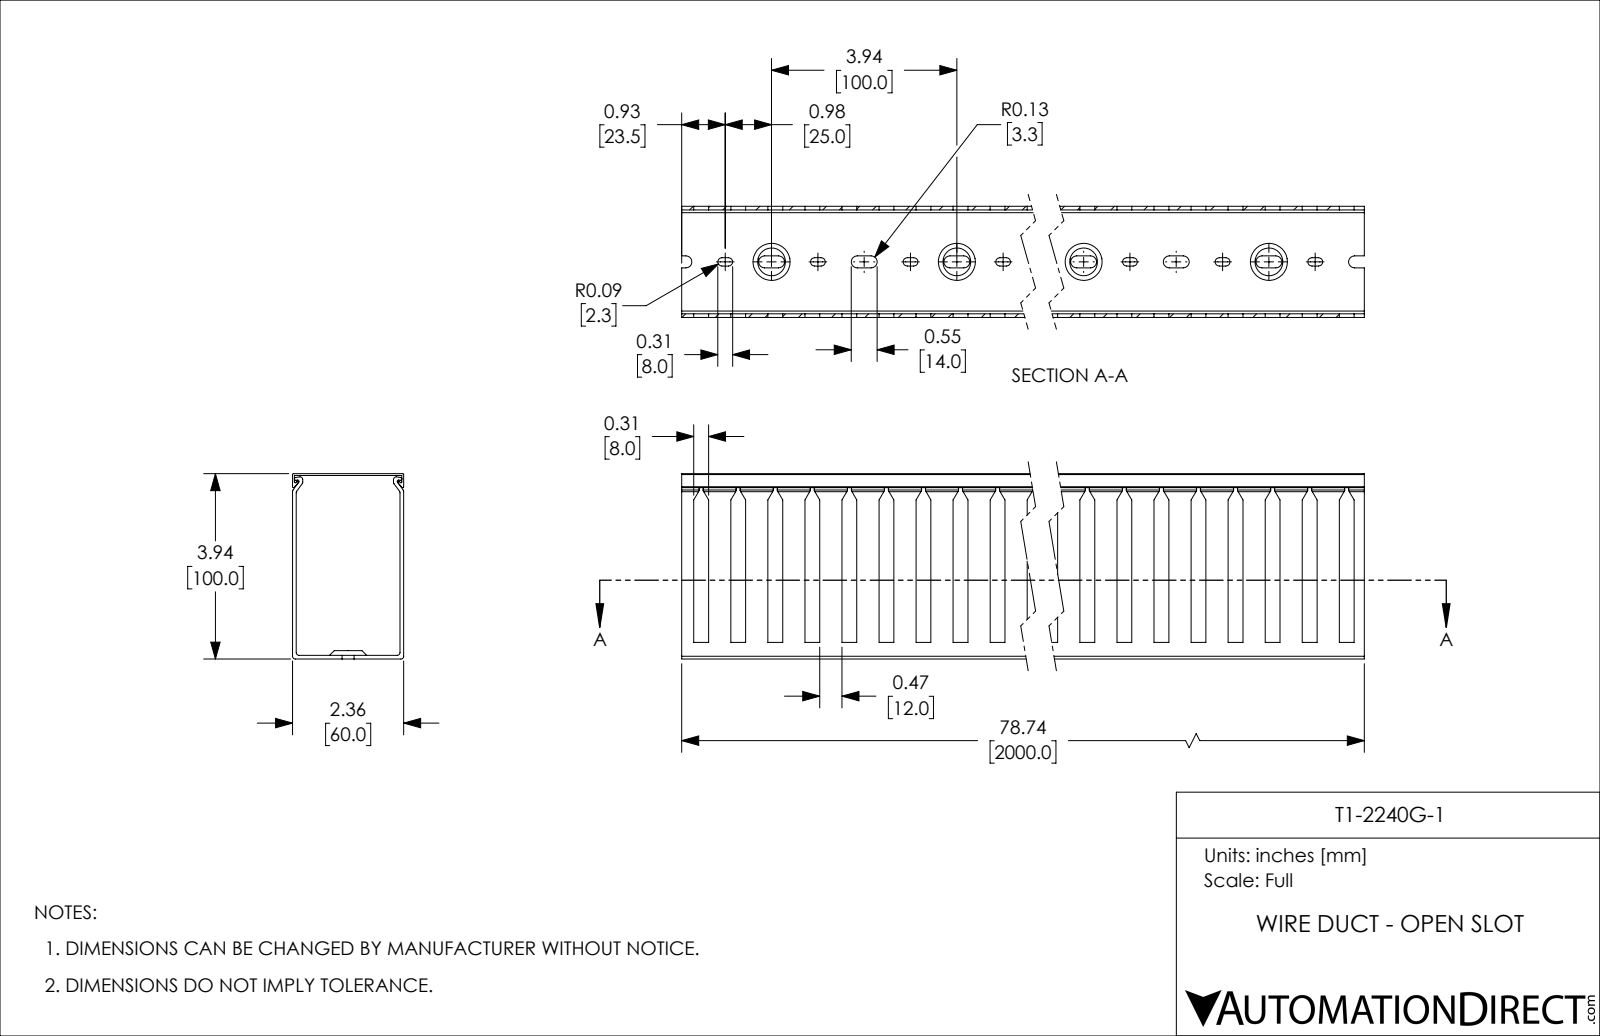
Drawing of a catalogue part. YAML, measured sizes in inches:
part_name: "T1-2240G-1"
step_written_by: "SolidWorks 2021 (CONFIG_CONTROL_DESIGN)"
units: inches
bodies: {solids: 2, faces: 1005, planar: 534, cylindrical: 431, other: 40}
overall_size: [78.74, 3.937, 2.362]
volume: 70.91
surface_area: 2049
partial_cylinders:
  - {radius: 0.089, count: 80}
  - {radius: 0.128, count: 80}
  - {radius: 0.059, count: 12}
  - {radius: 0.02, count: 8}
  - {radius: 0.03, count: 6}
face_to_face_distances: [0.079, 2.283, 2.362, 2.205, 0.039, 3.937, 3.898, 3.819, 3.858, 2.323]
